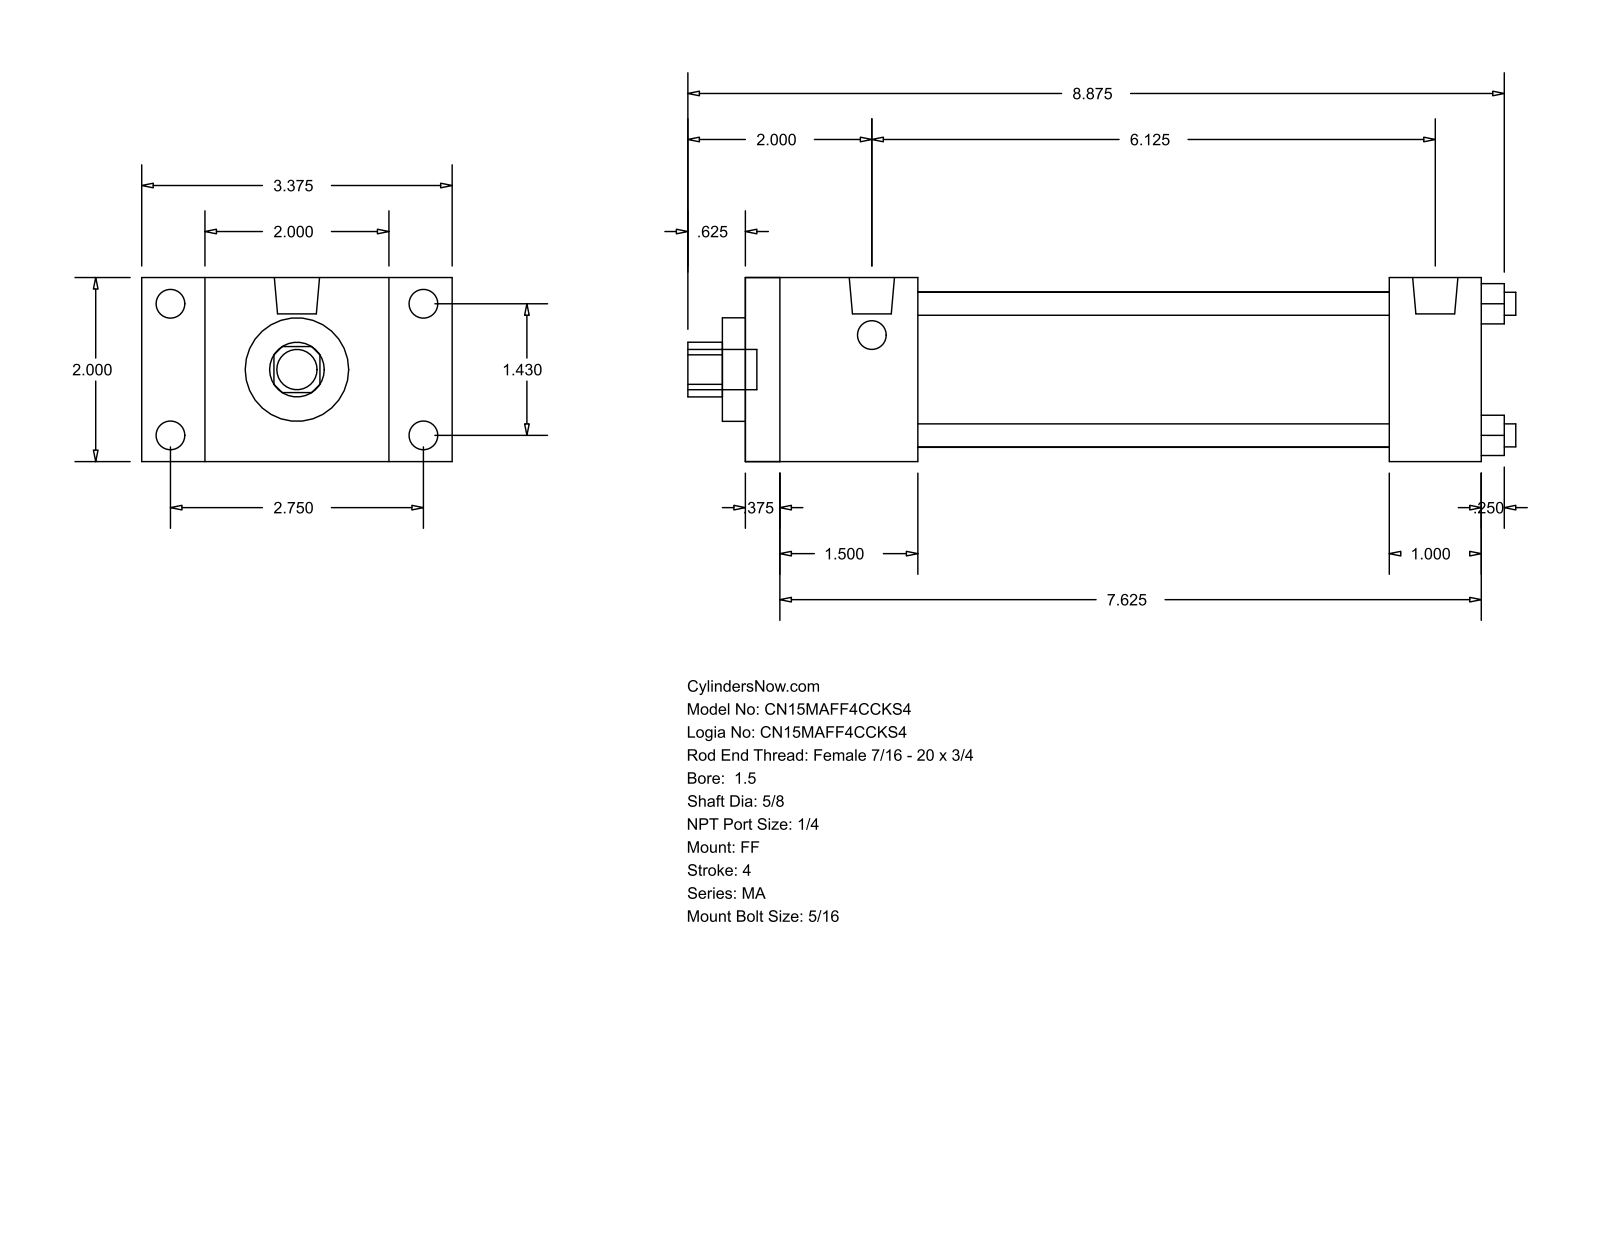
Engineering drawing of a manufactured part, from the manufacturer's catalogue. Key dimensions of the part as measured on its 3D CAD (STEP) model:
Part name (STEP PRODUCT): MA_FF__0150_0.625
STEP written by: GSSL Pune (CONFIG_CONTROL_DESIGN)
Units: millimetres
Bodies: 0 solids, 92 faces (64 planar, 28 cylindrical, 0 other)
Overall size (bounding box): 228.6 × 85.72 × 50.8
Round holes (diameter × count): ⌀6.35 ×4, ⌀15.88 ×1, ⌀28.57 ×1, ⌀42.93 ×1
Round bosses / shafts (diameter × count): ⌀7.94 ×8, ⌀12.49 ×2, ⌀11.11 ×1
Partial cylindrical surfaces — rounded edges, fillets, slot ends (radius × count): R7.54 ×1
Main face-to-face distances: 50.8, 203.19, 9.52, 193.67, 47.62, 177.8, 38.1, 168.28, 130.18, 155.57
Hole centre spacings: 25.68, 36.32, 51.36
